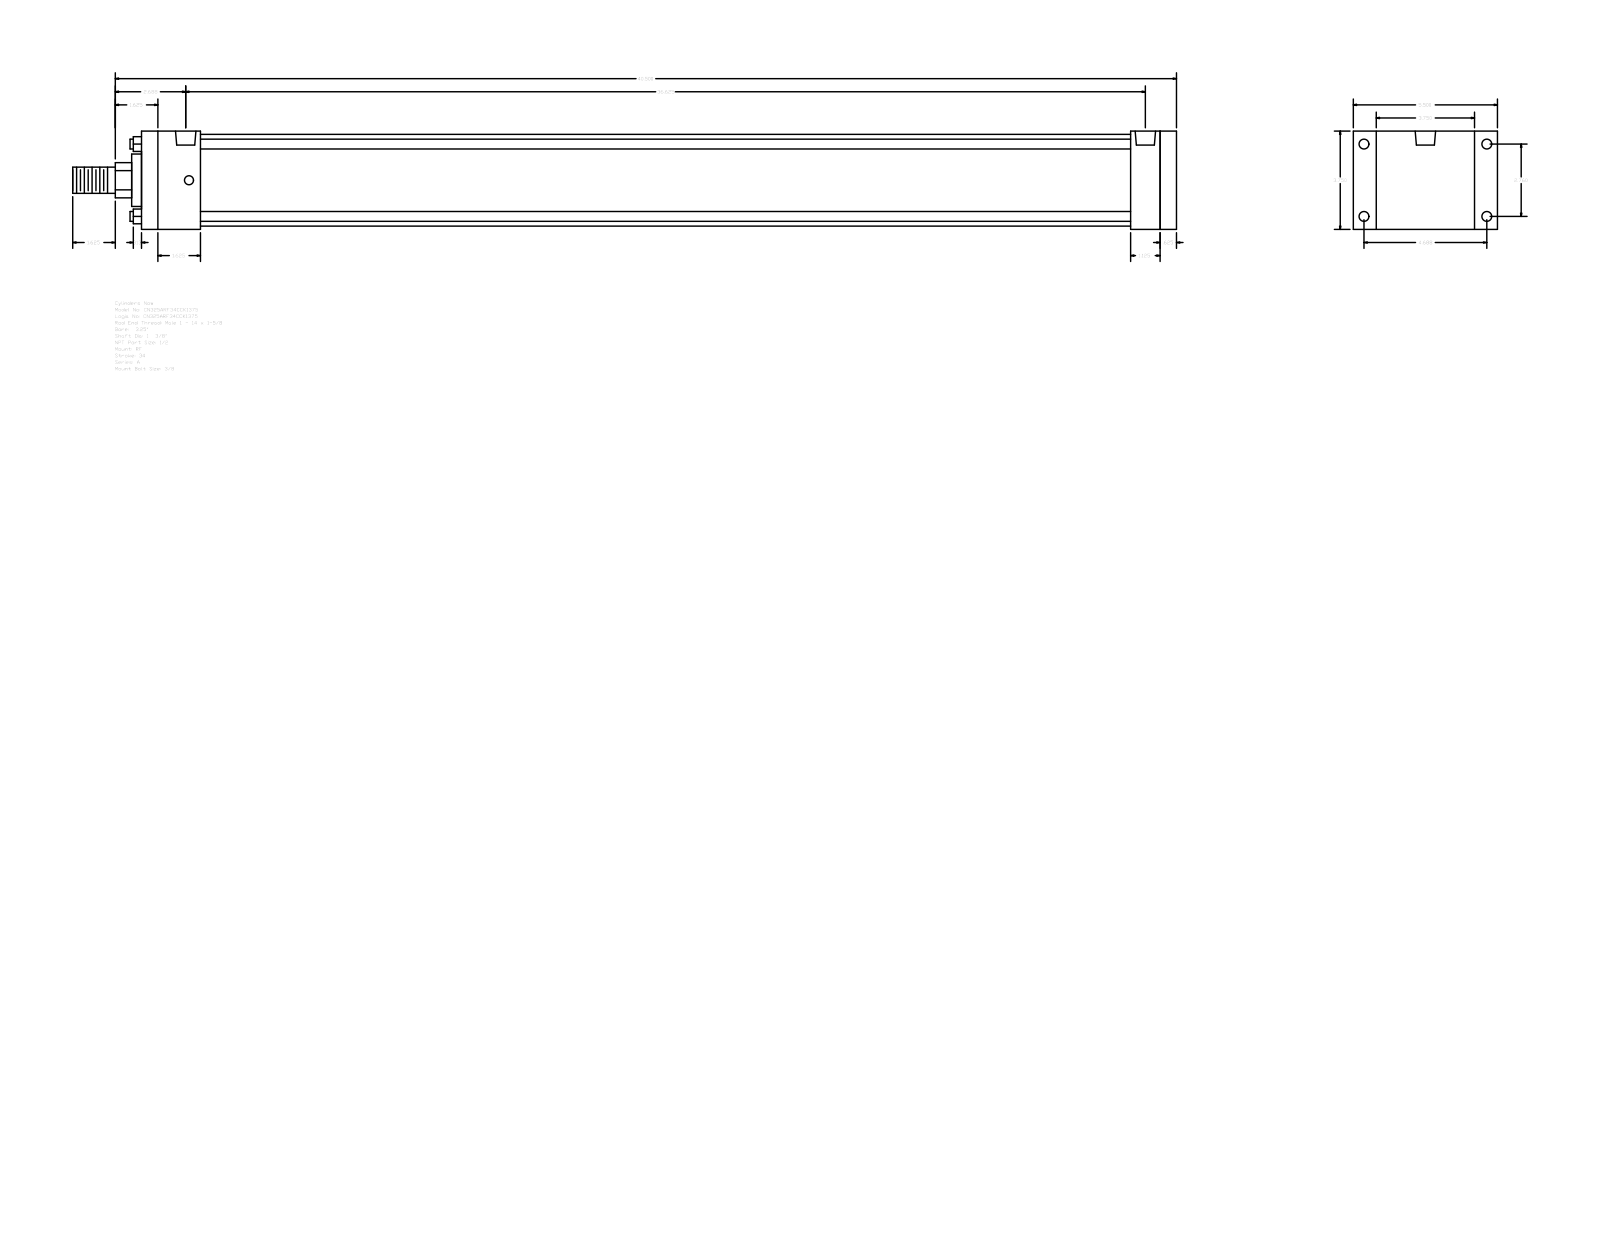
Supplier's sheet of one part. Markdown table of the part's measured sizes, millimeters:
| quantity | value |
| --- | --- |
| part name | A_RF__0325_1.375 |
| STEP written by | GSSL Pune (CONFIG_CONTROL_DESIGN) |
| units | millimeters |
| bodies | 0 solids, 92 faces (64 planar, 28 cylindrical, 0 other) |
| overall size | 1069.97 × 139.7 × 95.25 |
| round holes (diameter × count) | 8.73 × 4, 9.53 × 4, 19.77 × 2 |
| round bosses / shafts (diameter × count) | 9.53 × 4, 88.9 × 1, 50.8 × 1, 34.92 × 1, 25.4 × 1 |
| partial cylindrical surfaces (radius × count) | 17.06 × 1 |
| main face-to-face distances | 95.24, 1003.3, 987.43, 15.87, 57.15, 28.58, 22.23, 117.47, 958.85, 44.45 |
| hole center spacings | 3.18, 70.1, 119.06, 138.16, 923.92, 927.1, 930.28 |
